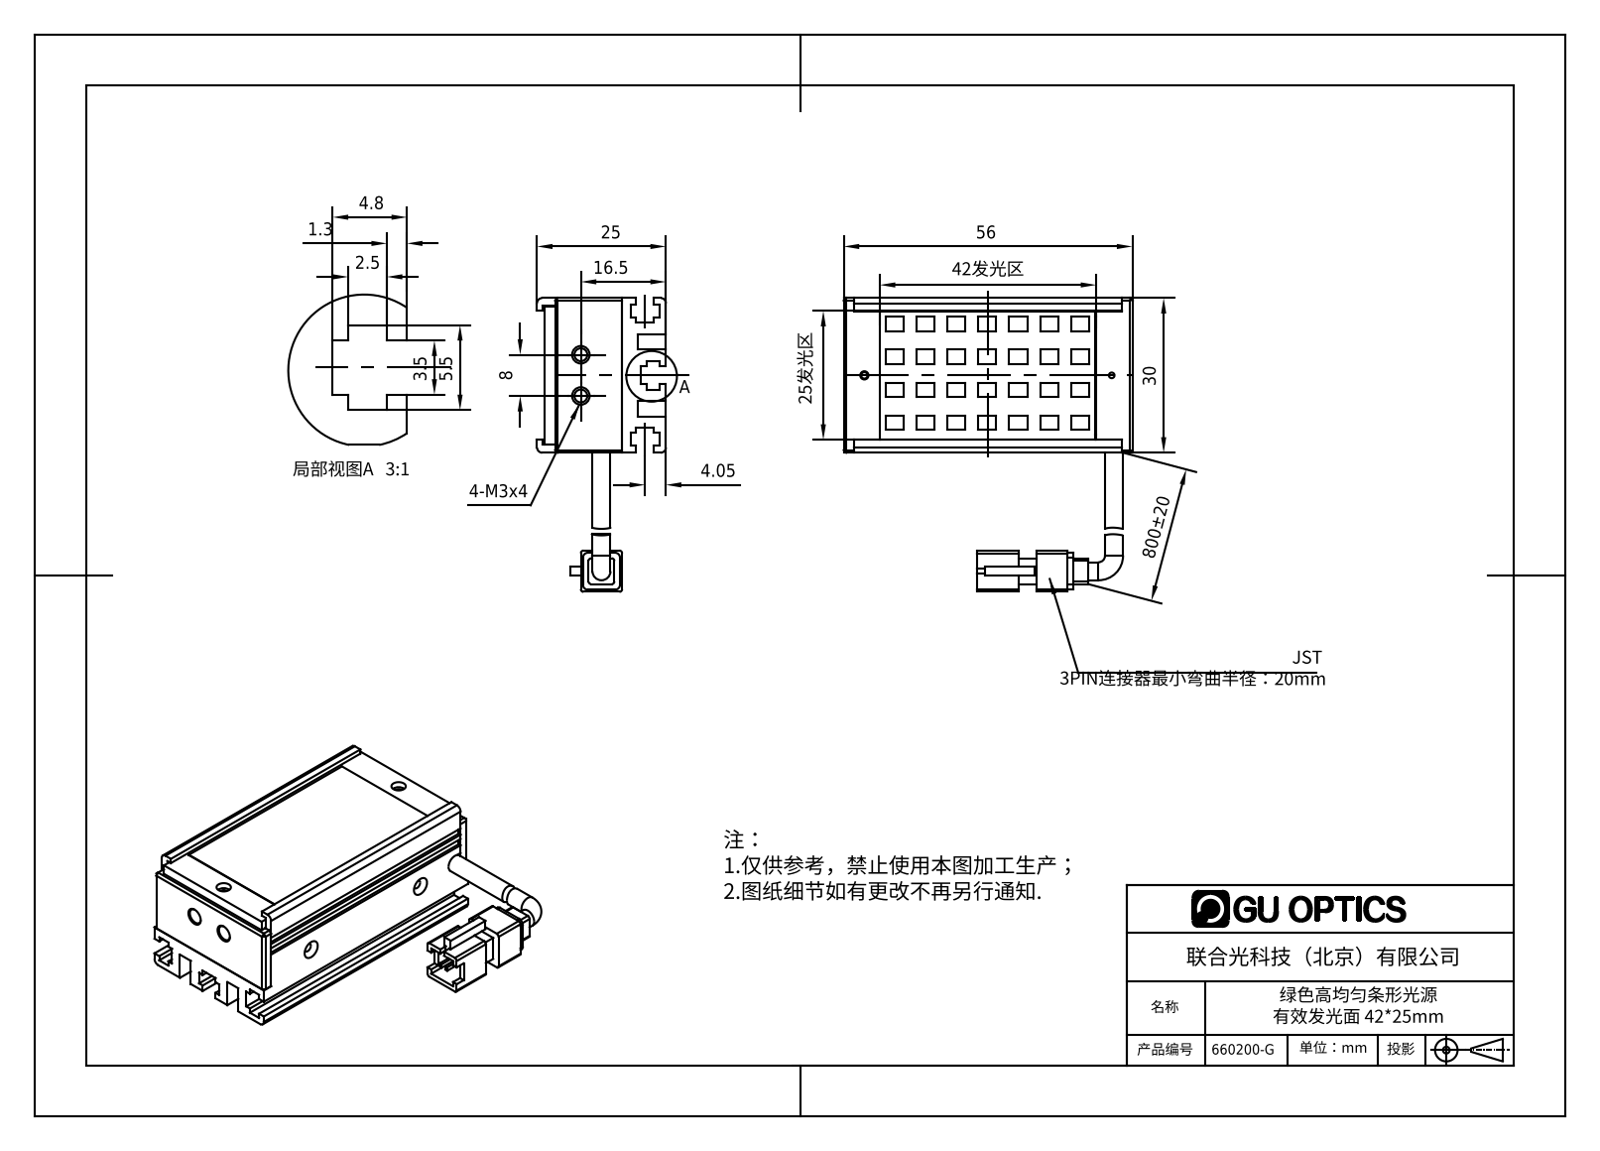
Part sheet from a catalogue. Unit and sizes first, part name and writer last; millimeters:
Units: millimetres
Overall size (bounding box): 57 × 56 × 25
Round holes (diameter × count): ⌀1.6 ×5, ⌀1.5 ×2, ⌀1.7 ×2, ⌀2.5 ×2, ⌀2.8 ×2, ⌀3 ×2, ⌀1.1 ×1, ⌀1.25 ×1, ⌀2 ×1
Round bosses / shafts (diameter × count): ⌀3.5 ×2
Partial cylindrical surfaces — rounded edges, fillets, slot ends (radius × count): R1 ×12, R0.5 ×8, R1.65 ×1
Main face-to-face distances: 1, 13, 2, 2.5, 7, 3, 4.5, 8.5, 2.1, 9.5
Hole centre spacings: 48, 7, 9.01, 11.16, 39, 39.55, 48.51, 8
Volume: 22 597 mm³ · Surface area: 22 386 mm²
Bodies: 6 solids, 584 faces (398 planar, 83 cylindrical, 103 other)
Part name (STEP PRODUCT): 660200-G
STEP written by: SolidWorks 2016 (AUTOMOTIVE_DESIGN)
